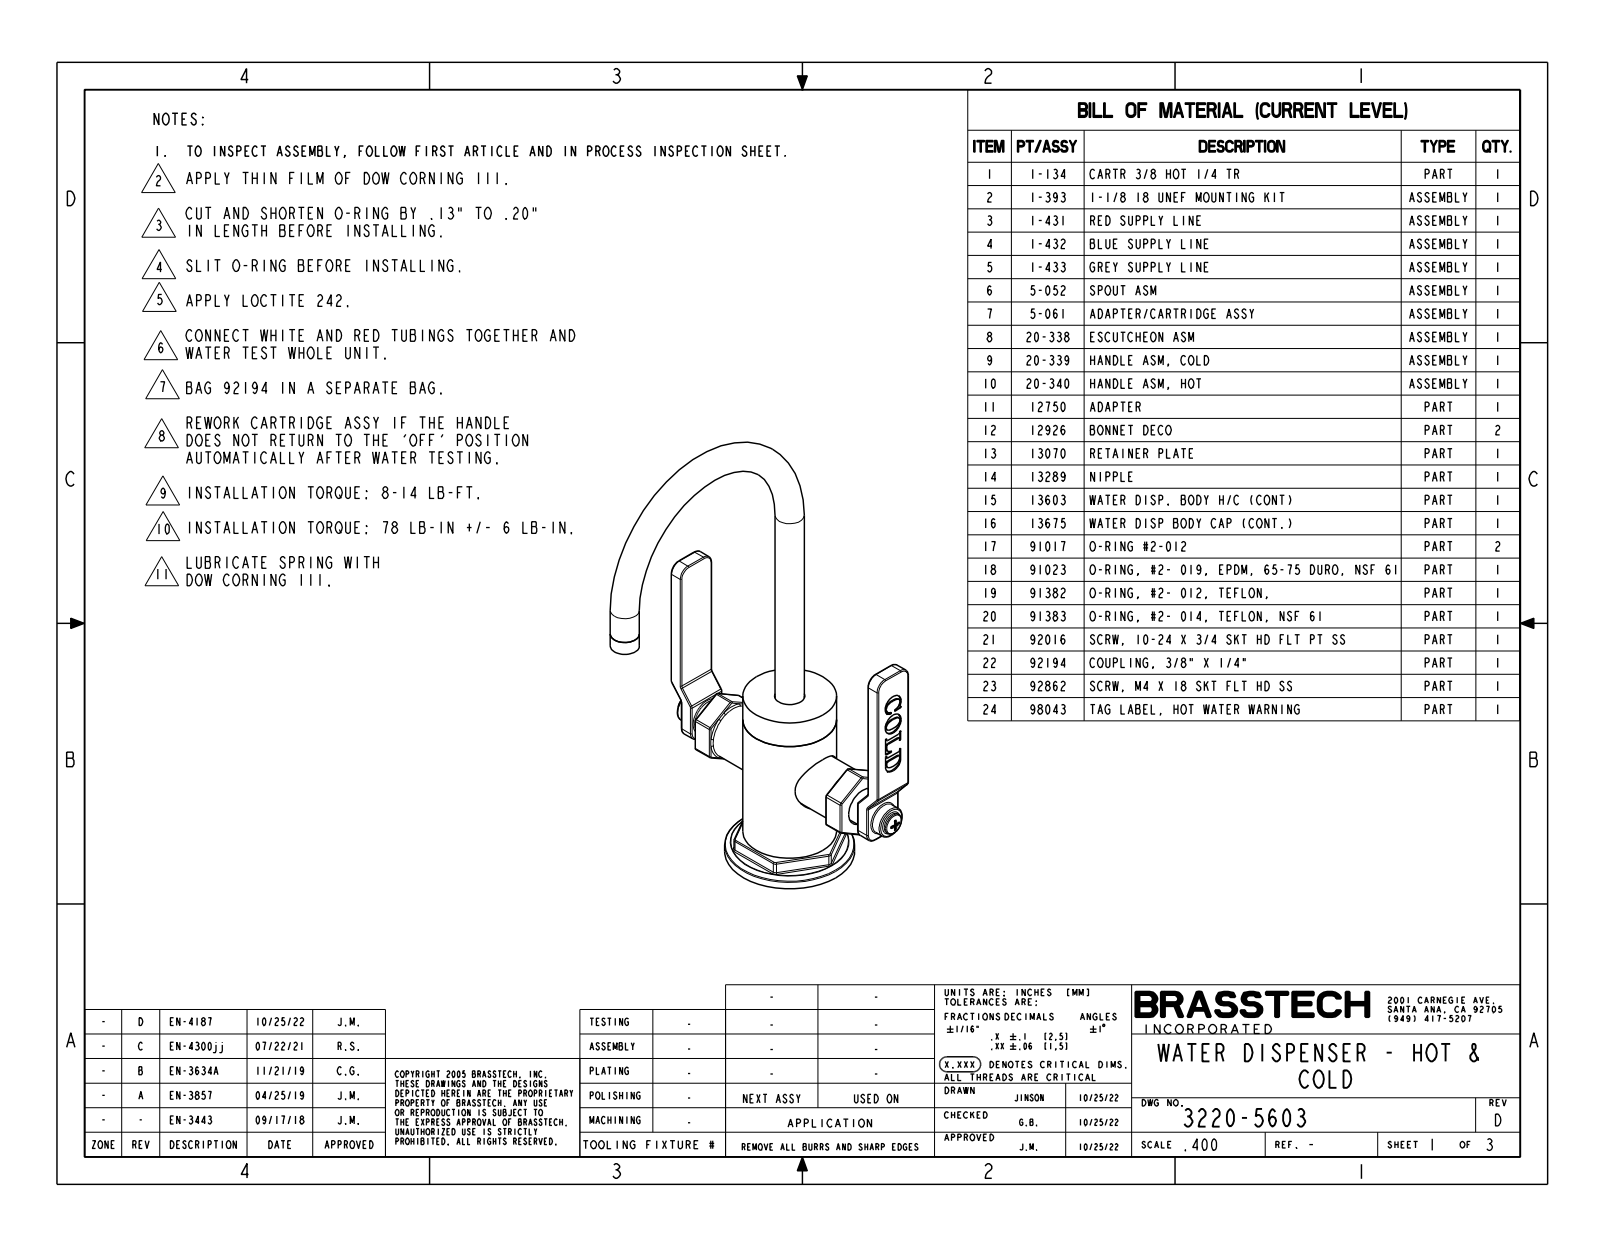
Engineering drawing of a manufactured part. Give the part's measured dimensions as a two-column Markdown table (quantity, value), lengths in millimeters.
| quantity | value |
| --- | --- |
| part name | 3220-5603 |
| STEP written by | CREO PARAMETRIC BY PTC INC, 2018400 (CONFIG_CONTROL_DESIGN) |
| units | millimeters |
| bodies | 1 solid, 719 faces (187 planar, 178 cylindrical, 354 other) |
| overall size | 235.6 × 136.3 × 130.8 |
| volume | 203 500 mm³ |
| surface area | 42 420 mm² |
| round holes (diameter × count) | 25.4 × 1 |
| round bosses / shafts (diameter × count) | 12.7 × 2, 56.6 × 1, 40.9 × 1, 24.6 × 1, 15.9 × 1, 14 × 1, 9.5 × 1 |
| partial cylindrical surfaces (radius × count) | 0.5 × 68, 0.3 × 40, 1.5 × 14, 1 × 6, 4.7 × 4 |
| main face-to-face distances | 6.4, 121.3, 115, 83.2, 127.7, 19.1, 3.9, 23, 26.9, 18.7 |
